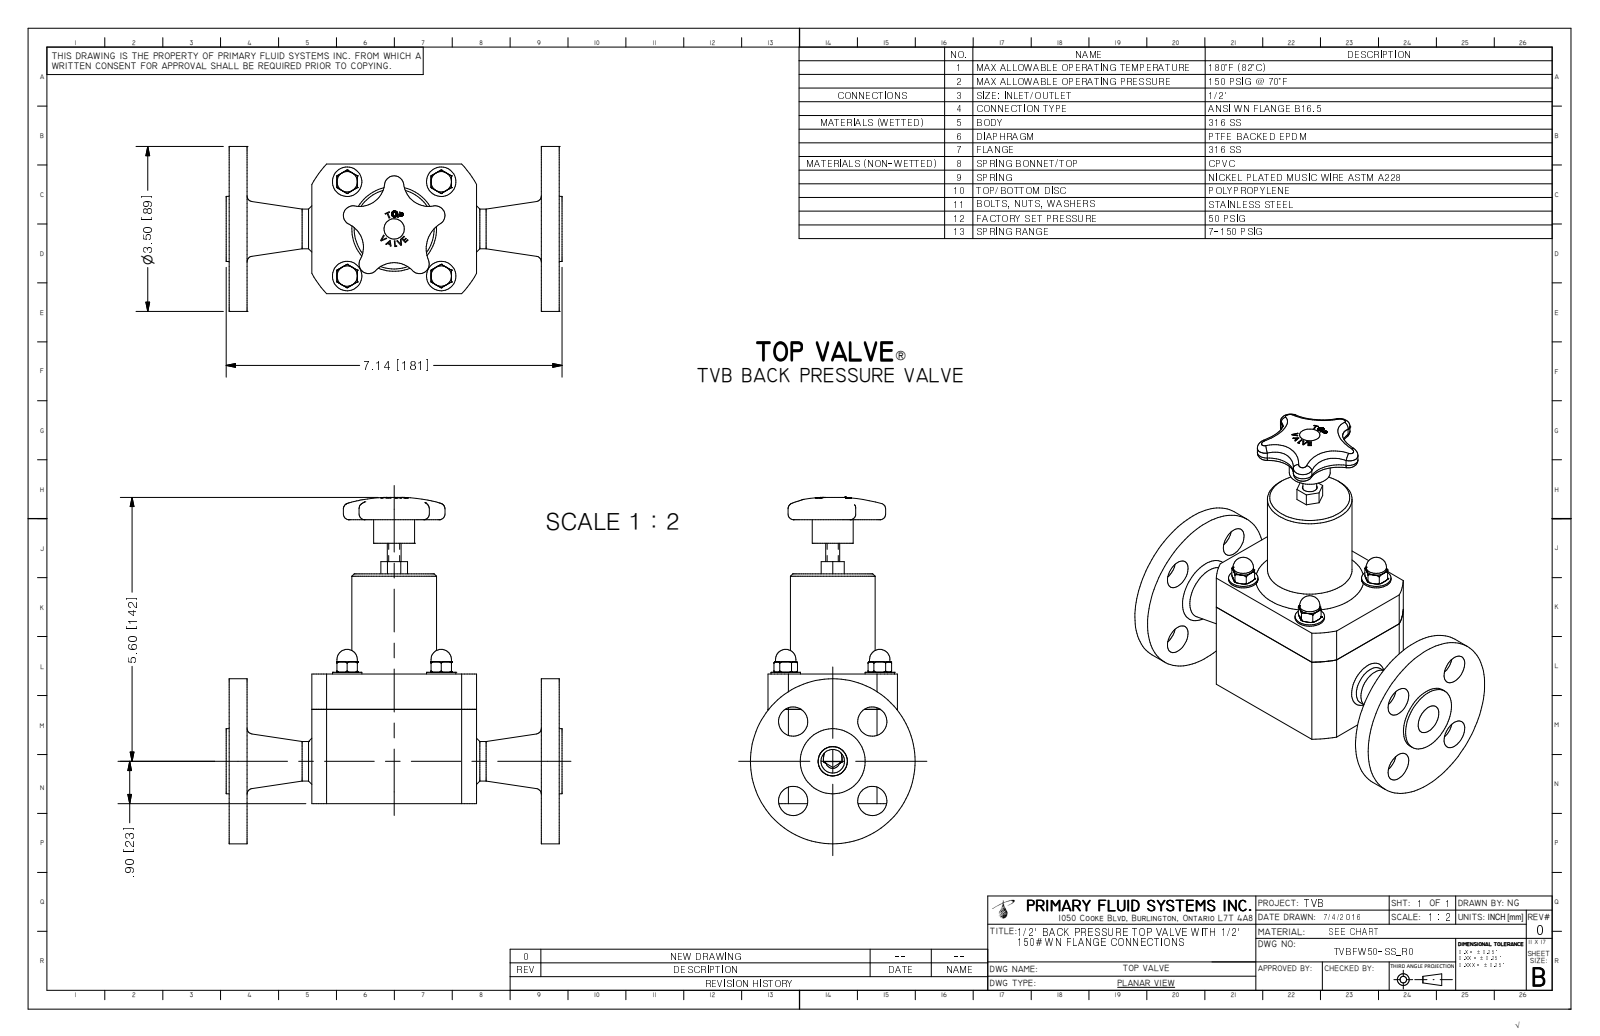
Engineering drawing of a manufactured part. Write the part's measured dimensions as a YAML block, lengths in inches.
part_name: "TVBFW50-SS-R0"
step_written_by: "Autodesk Inventor 2009 (AUTOMOTIVE_DESIGN)"
units: inches
bodies: {solids: 1, faces: 371, planar: 160, cylindrical: 59, other: 152}
overall_size: [7.347, 7.14, 3.5]
volume: 40.39
surface_area: 138.7
round_holes:
  - {diameter: 0.175, count: 4}
  - {diameter: 0.62, count: 4}
  - {diameter: 0.622, count: 1}
round_bosses_or_shafts:
  - {diameter: 0.625, count: 4}
  - {diameter: 0.433, count: 4}
  - {diameter: 0.375, count: 4}
  - {diameter: 3.5, count: 1}
  - {diameter: 1.8, count: 1}
  - {diameter: 1.38, count: 1}
  - {diameter: 0.87, count: 1}
  - {diameter: 0.84, count: 1}
partial_cylinders:
  - {radius: 0.085, count: 5}
  - {radius: 0.205, count: 5}
  - {radius: 0.536, count: 4}
  - {radius: 0.656, count: 4}
  - {radius: 0.625, count: 1}
  - {radius: 0.745, count: 1}
  - {radius: 1.988, count: 1}
face_to_face_distances: [0.38, 6.635, 1.757, 5.257, 1.378, 4.878, 2.75, 7.015, 6.255, 3.5]
hole_center_spacings: [1.19, 1.683, 2, 2.38, 2.828]
